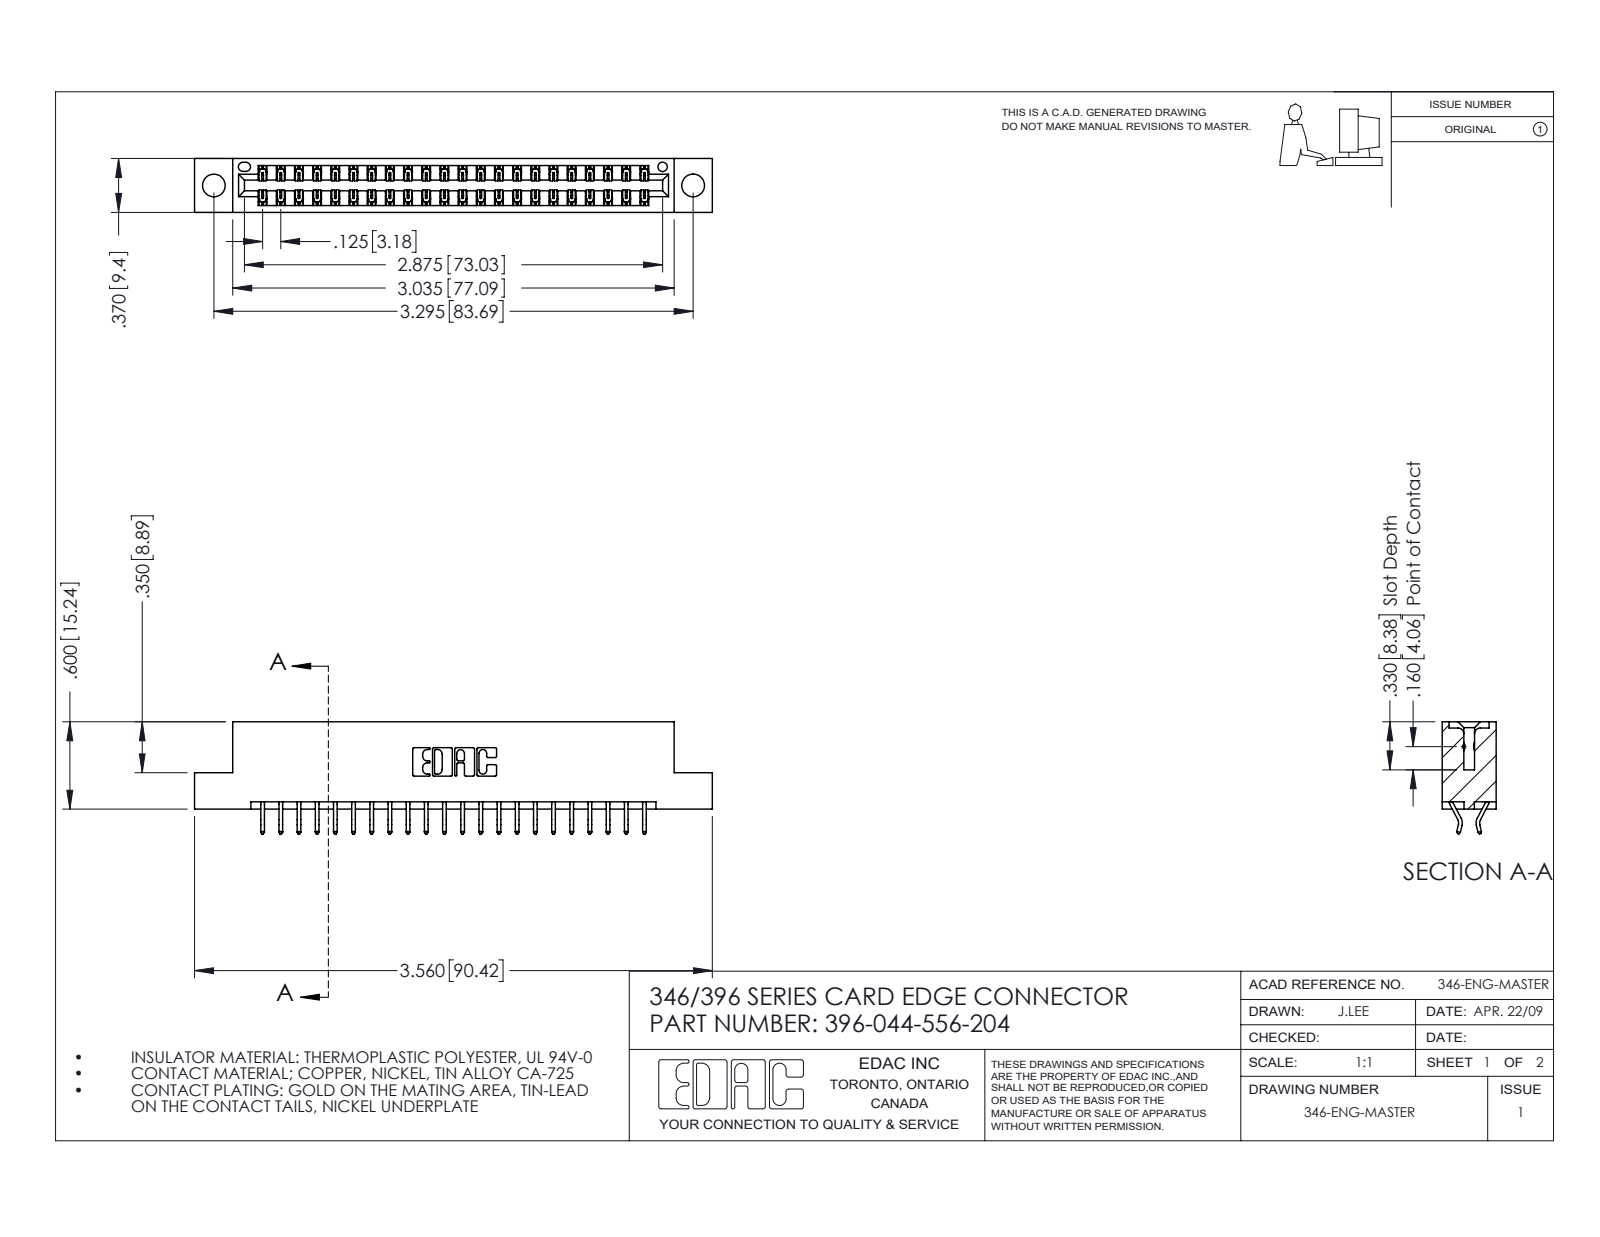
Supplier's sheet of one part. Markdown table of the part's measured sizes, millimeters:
| quantity | value |
| --- | --- |
| part name | 345-292-001_556 Tail; 346 Part_Flush Mounting Lugs - 0.156 Dia-TH; 396-044-556-204 |
| STEP written by | SolidWorks 2016 (CONFIG_CONTROL_DESIGN) |
| units | millimeters |
| bodies | 45 solids, 2674 faces (1792 planar, 882 cylindrical, 0 other) |
| overall size | 90.4 × 19.6 × 9.4 |
| volume | 8 570 mm³ |
| surface area | 11 240 mm² |
| round holes (diameter × count) | 4 × 2, 1.6 × 1 |
| partial cylindrical surfaces (radius × count) | 0.2 × 66, 0.3 × 22, 0.2 × 6, 0.8 × 6, 0.7 × 3, 0.3 × 2, 0.4 × 2, 0.6 × 2 |
| main face-to-face distances | 1.2, 8.2, 6.4, 9.4, 0.6, 1.8, 7.6, 7, 3.8, 5.6 |
| hole center spacings | 6.2, 78.4, 83.7 |
